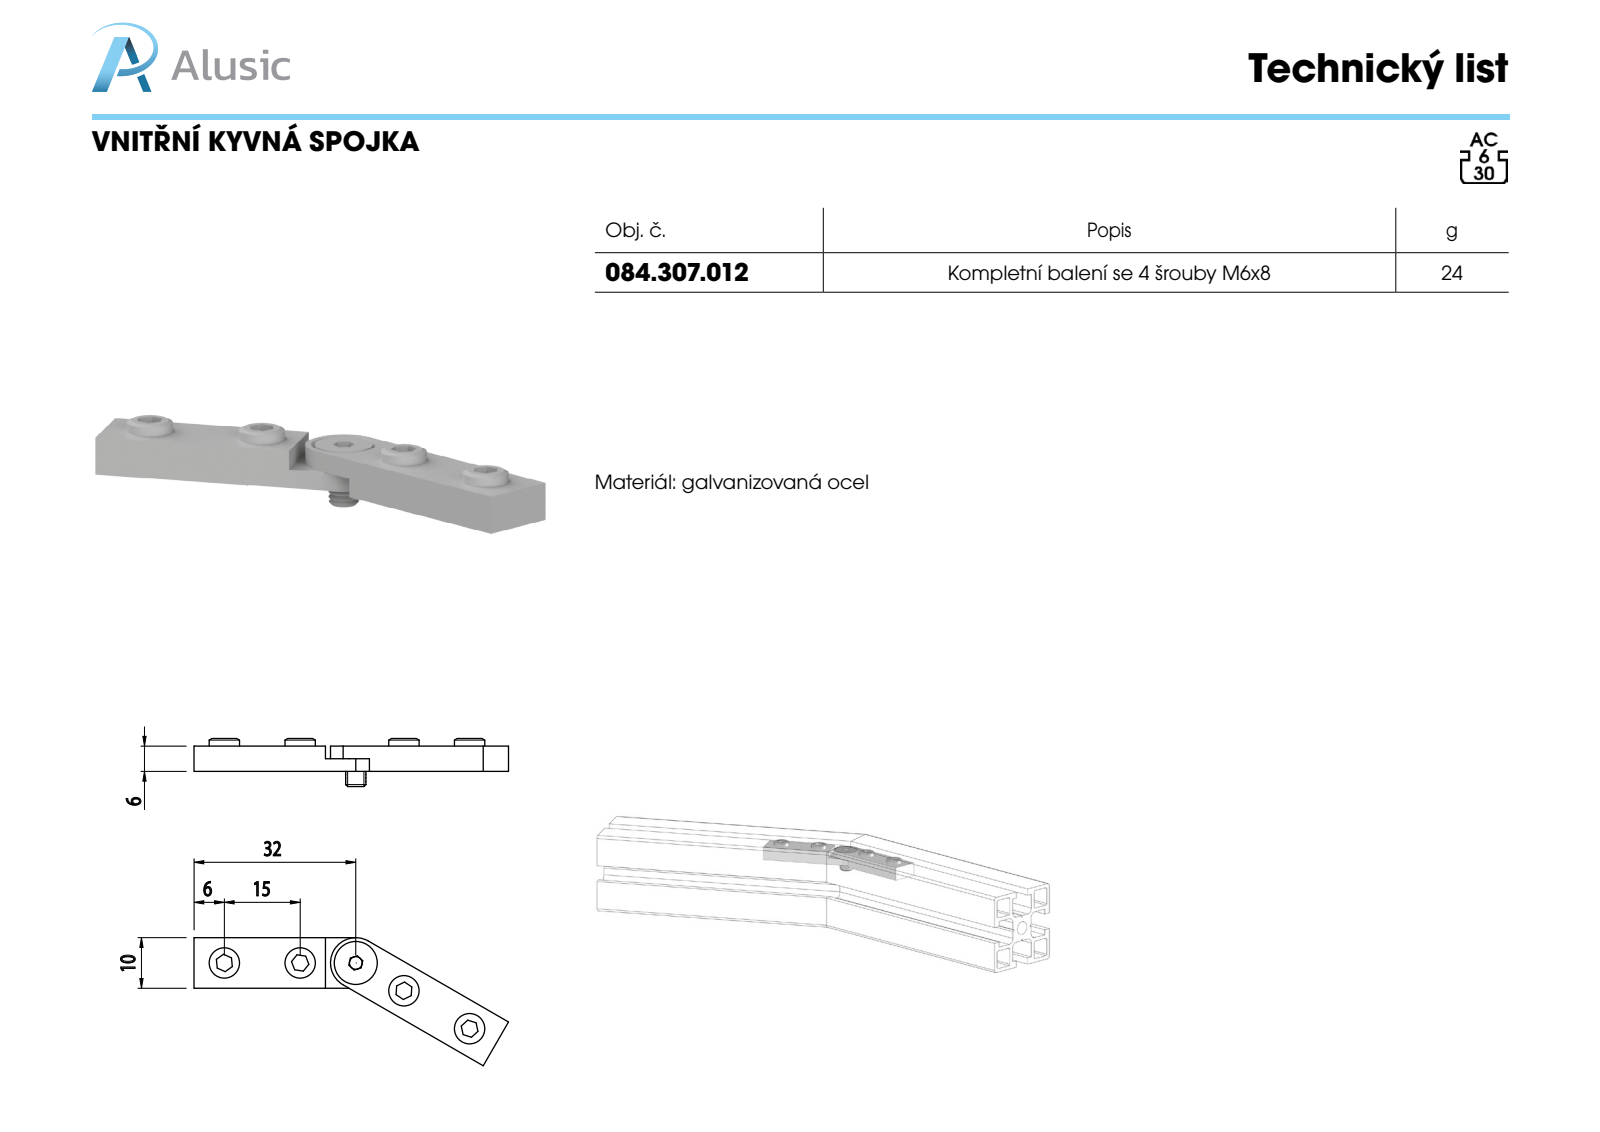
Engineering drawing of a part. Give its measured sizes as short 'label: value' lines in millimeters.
name: socket set screw cone point_iso_ISO 4027 - M6 x 5-N; 084.307.012; Socket Countersunk Head Screw_ALUSIC_ISO 10642 - M4 x 8 --- 8S; 084.307.012B (+1 more)
written by: SolidWorks 2011 (CONFIG_CONTROL_DESIGN)
unit: mm
bodies: 7 solids, 142 faces (60 planar, 36 cylindrical, 46 other)
size: 62.21 × 25.33 × 9.5
volume: 3 104 mm³; area: 3 177 mm²
holes: 4× ⌀5, 1× ⌀3.3, 1× ⌀4.5
bosses: 4× ⌀6, 1× ⌀10, 1× ⌀7.53, 1× ⌀4
face distances: 5, 2.5, 10, 2, 3, 26, 6.5, 1.5, 4, 4.5
hole spacings: 11, 15, 26, 35.95, 21.25, 50.23
